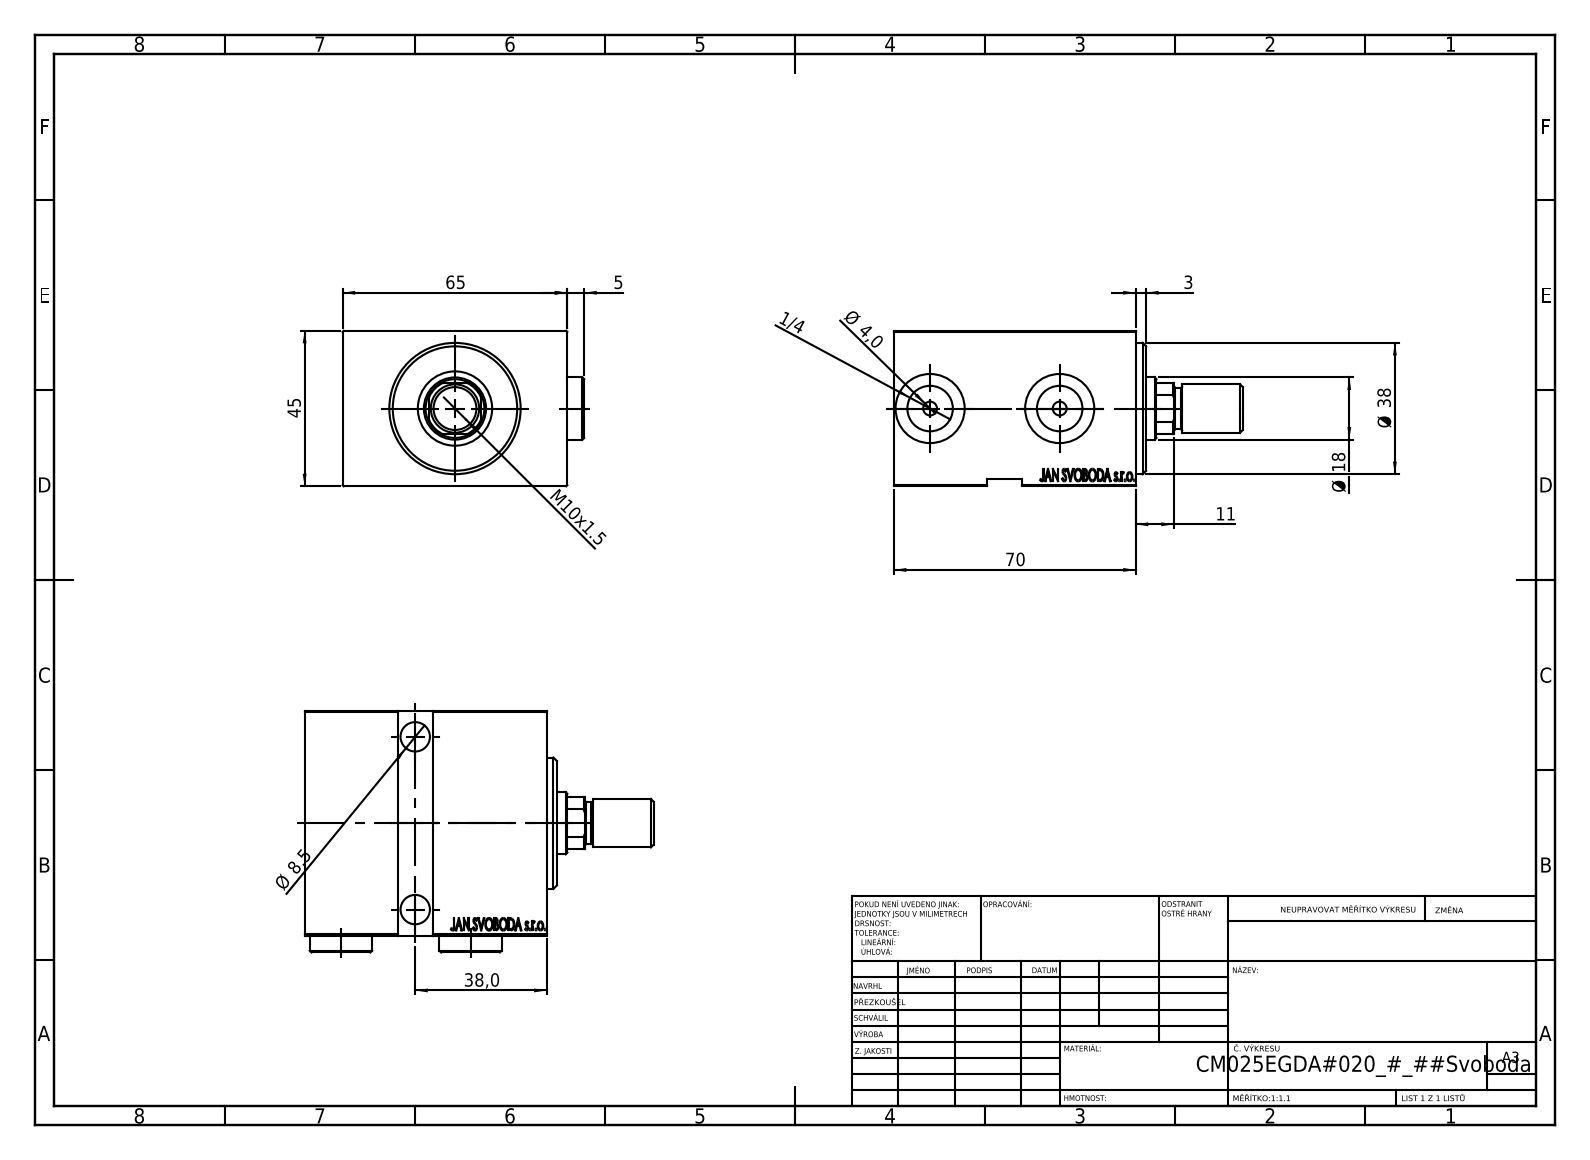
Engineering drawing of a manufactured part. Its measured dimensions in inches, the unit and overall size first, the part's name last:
Units: inches
Overall size (bounding box): 3.976 × 2.752 × 1.772
Round holes (diameter × count): ⌀0.335 ×3, ⌀0.157 ×2, ⌀0.518 ×2, ⌀0.531 ×2, ⌀0.787 ×2, ⌀0.709 ×1, ⌀0.846 ×1, ⌀0.984 ×1, ⌀1.378 ×1
Round bosses / shafts (diameter × count): ⌀0.709 ×2, ⌀1.496 ×1, ⌀1.063 ×1, ⌀0.551 ×1, ⌀0.472 ×1
Partial cylindrical surfaces — rounded edges, fillets, slot ends (radius × count): R0.335 ×1
Main face-to-face distances: 1.772, 2.559, 2.756, 0.197, 0.315, 2.555, 2.52, 0.118, 0.236, 2.323
Hole centre spacings: 1.476, 1.969
Volume: 11.78 in³ · Surface area: 68.51 in²
Bodies: 6 solids, 913 faces (445 planar, 64 cylindrical, 404 other)
Part name (STEP PRODUCT): V450CM_VC_B; V450CM_MALE_METRIC; V450CM_E_VCP; Zatka_OIL_PORT (+1 more)
STEP written by: SolidWorks 2019 (CONFIG_CONTROL_DESIGN)
